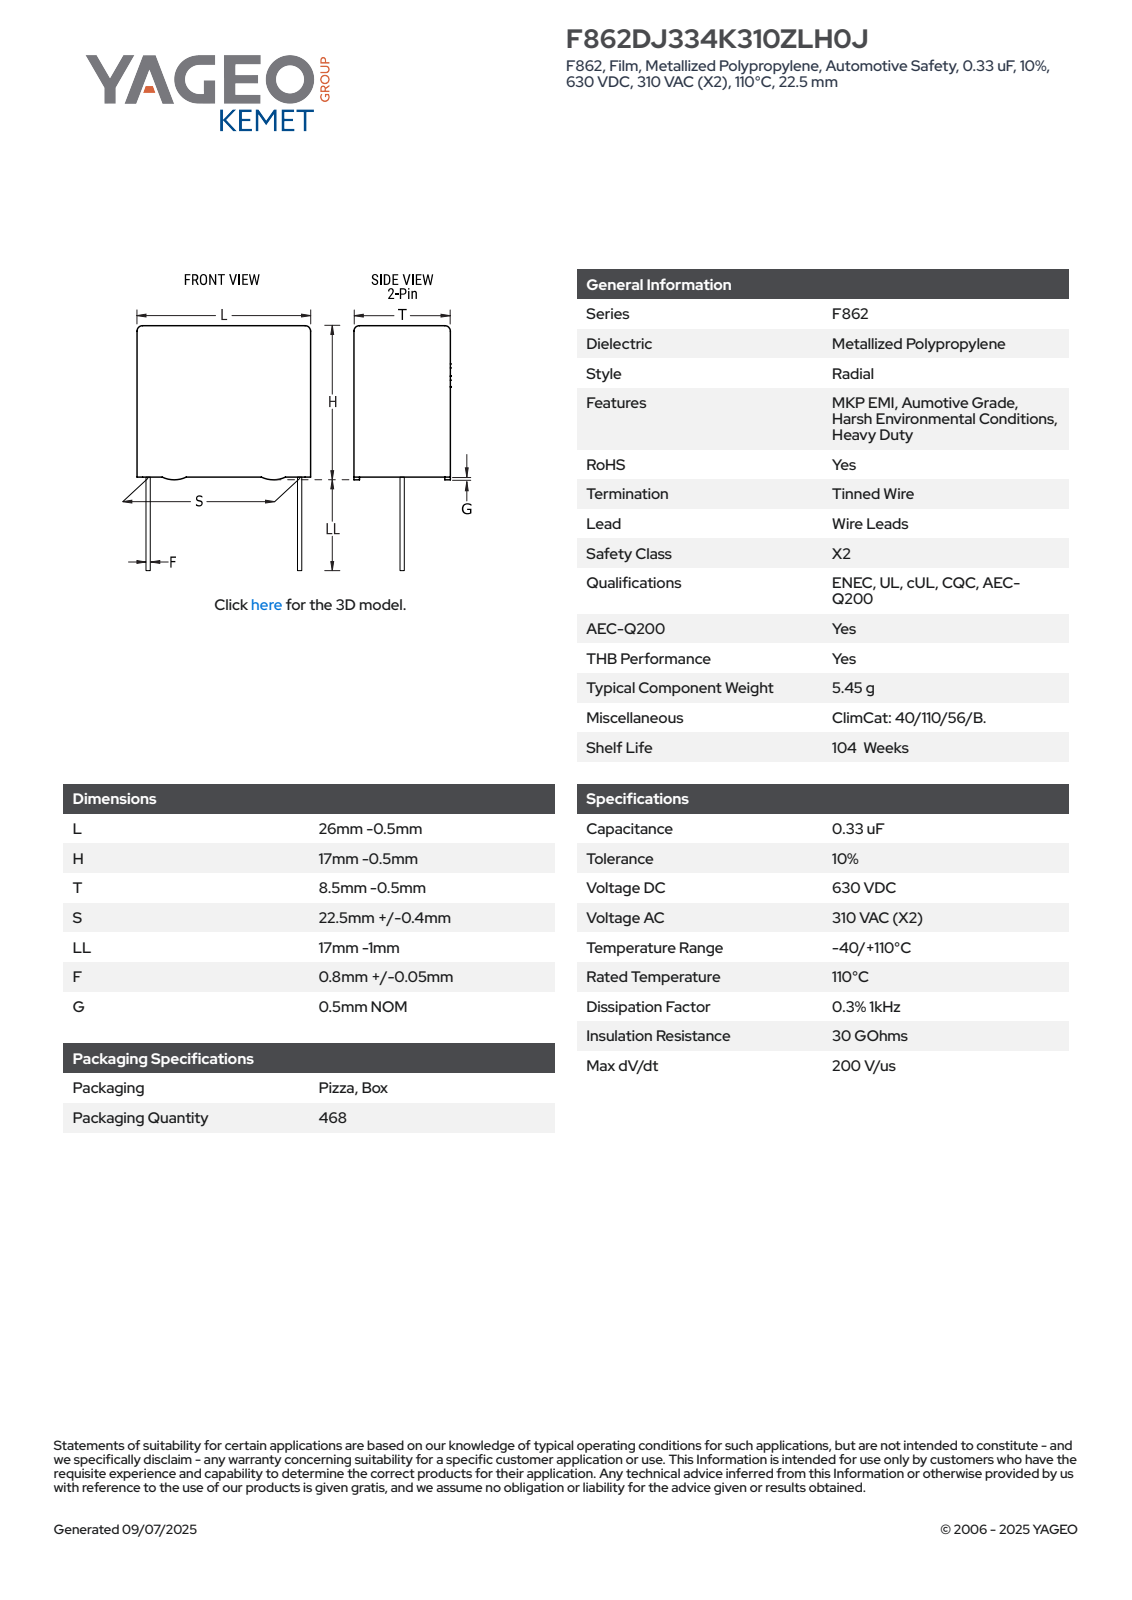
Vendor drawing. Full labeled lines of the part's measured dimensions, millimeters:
Part name (STEP PRODUCT): CFR_RBG_26X17X8.5_L25.5H16.5T8S22.5LL16F0.85G0.5
STEP written by: SolidWorks 2014 (AUTOMOTIVE_DESIGN)
Units: millimetres
Bodies: 4 solids, 89 faces (81 planar, 8 cylindrical, 0 other)
Overall size (bounding box): 32.5 × 25.5 × 8.01
Volume: 3 283 mm³ · Surface area: 1 641 mm²
Round bosses / shafts (diameter × count): ⌀0.85 ×2
Partial cylindrical surfaces — rounded edges, fillets, slot ends (radius × count): R0.5 ×4
Main face-to-face distances: 8, 16, 25.5, 8.01, 16.5, 0.46, 7.54, 0.5, 0.47, 7.08
